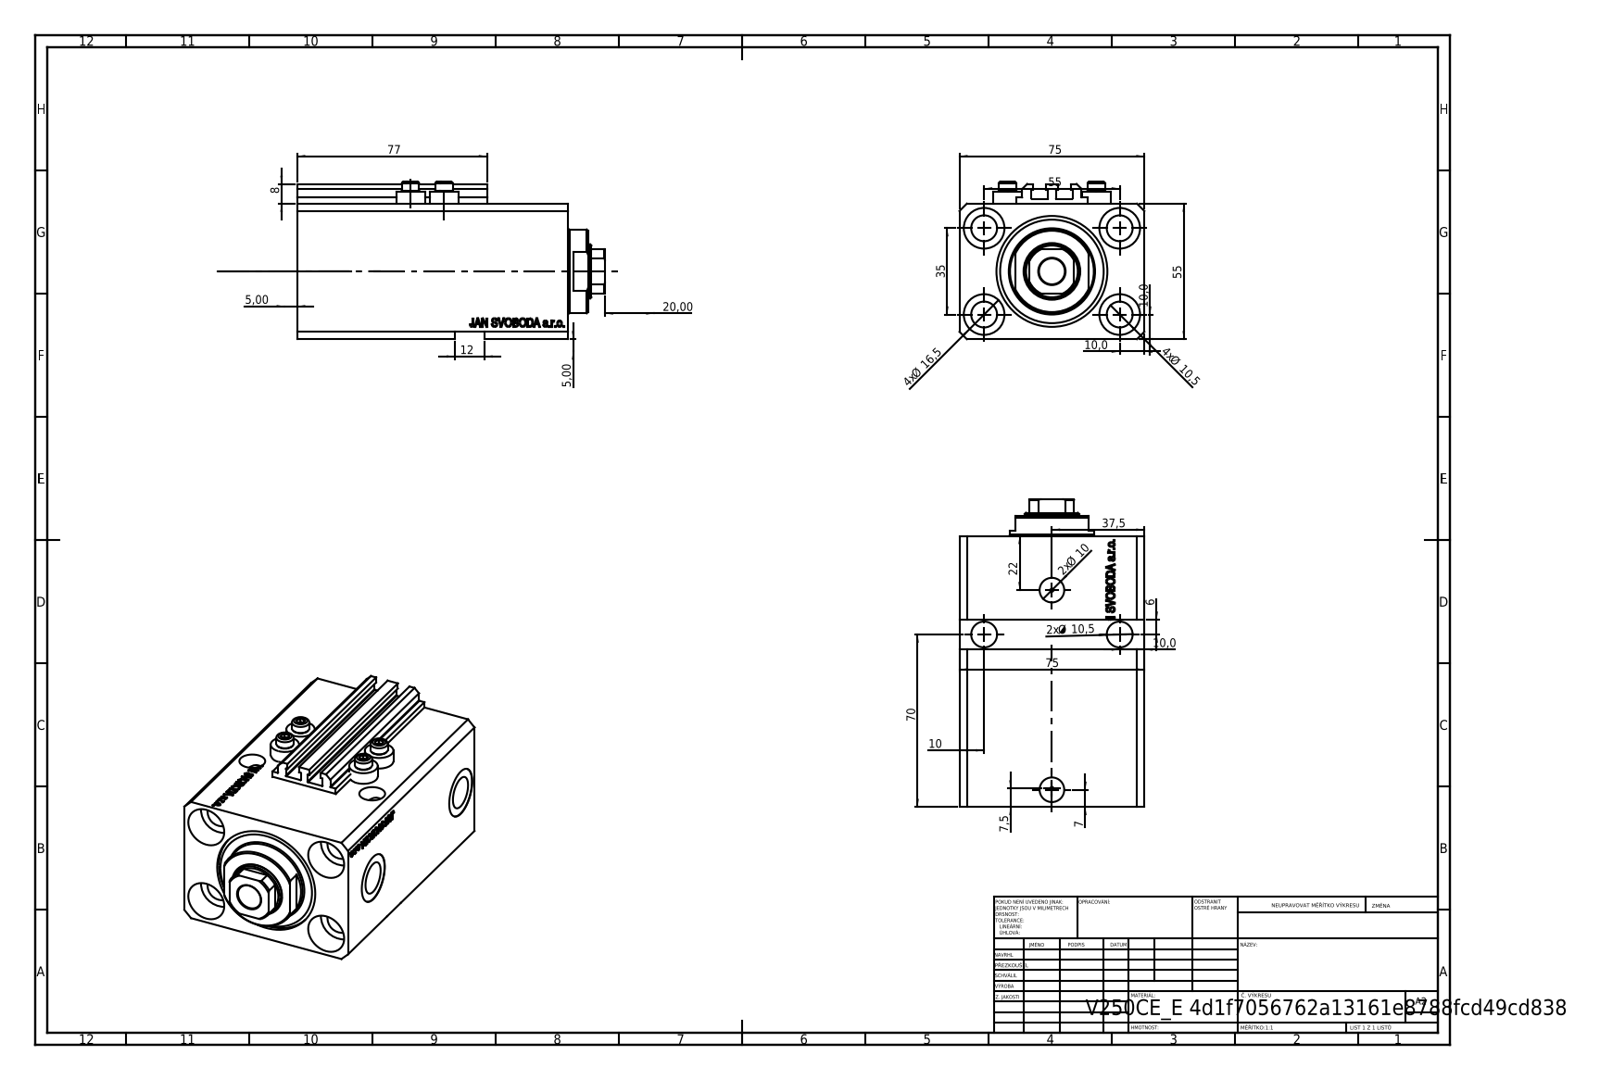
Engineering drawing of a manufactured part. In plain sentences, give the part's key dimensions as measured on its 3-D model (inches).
The part is named "V250CE_C_VCP; V250CE_E; V250CE_VC_E; ALLEN BOLT V250CE". Its 3-D file was written by "SolidWorks 2019 (CONFIG_CONTROL_DESIGN)". It is 8 solids with 1064 faces: 514 planar, 126 cylindrical and 424 other. Overall it measures 4.917 by 2.953 by 2.52 inches. Its volume is 23.66 cubic inches and its surface area 149.9 square inches. Round holes: 7 of diameter 0.413, 4 of diameter 0.049, 4 of diameter 0.157, 4 of diameter 0.65, 2 of diameter 0.394, 2 of diameter 0.518, 2 of diameter 0.787, 1 of diameter 0.866, 1 of diameter 1.26, 1 of diameter 1.772. Round bosses or shafts: 4 of diameter 0.457, 4 of diameter 0.276, 1 of diameter 1.339. Partial cylindrical surfaces (rounded edges, fillets, slot ends): 10 of radius 0.008, 1 of radius 0.413. The main face-to-face distances are 2.165, 2.953, 4.331, 3.264, 1.067, 0.118, 0.39, 2.874, 3.941, 2.244. The hole center spacings are 1.283, 2.165, 0.535, 0.555, 1.016, 1.294, 1.324, 1.378.
